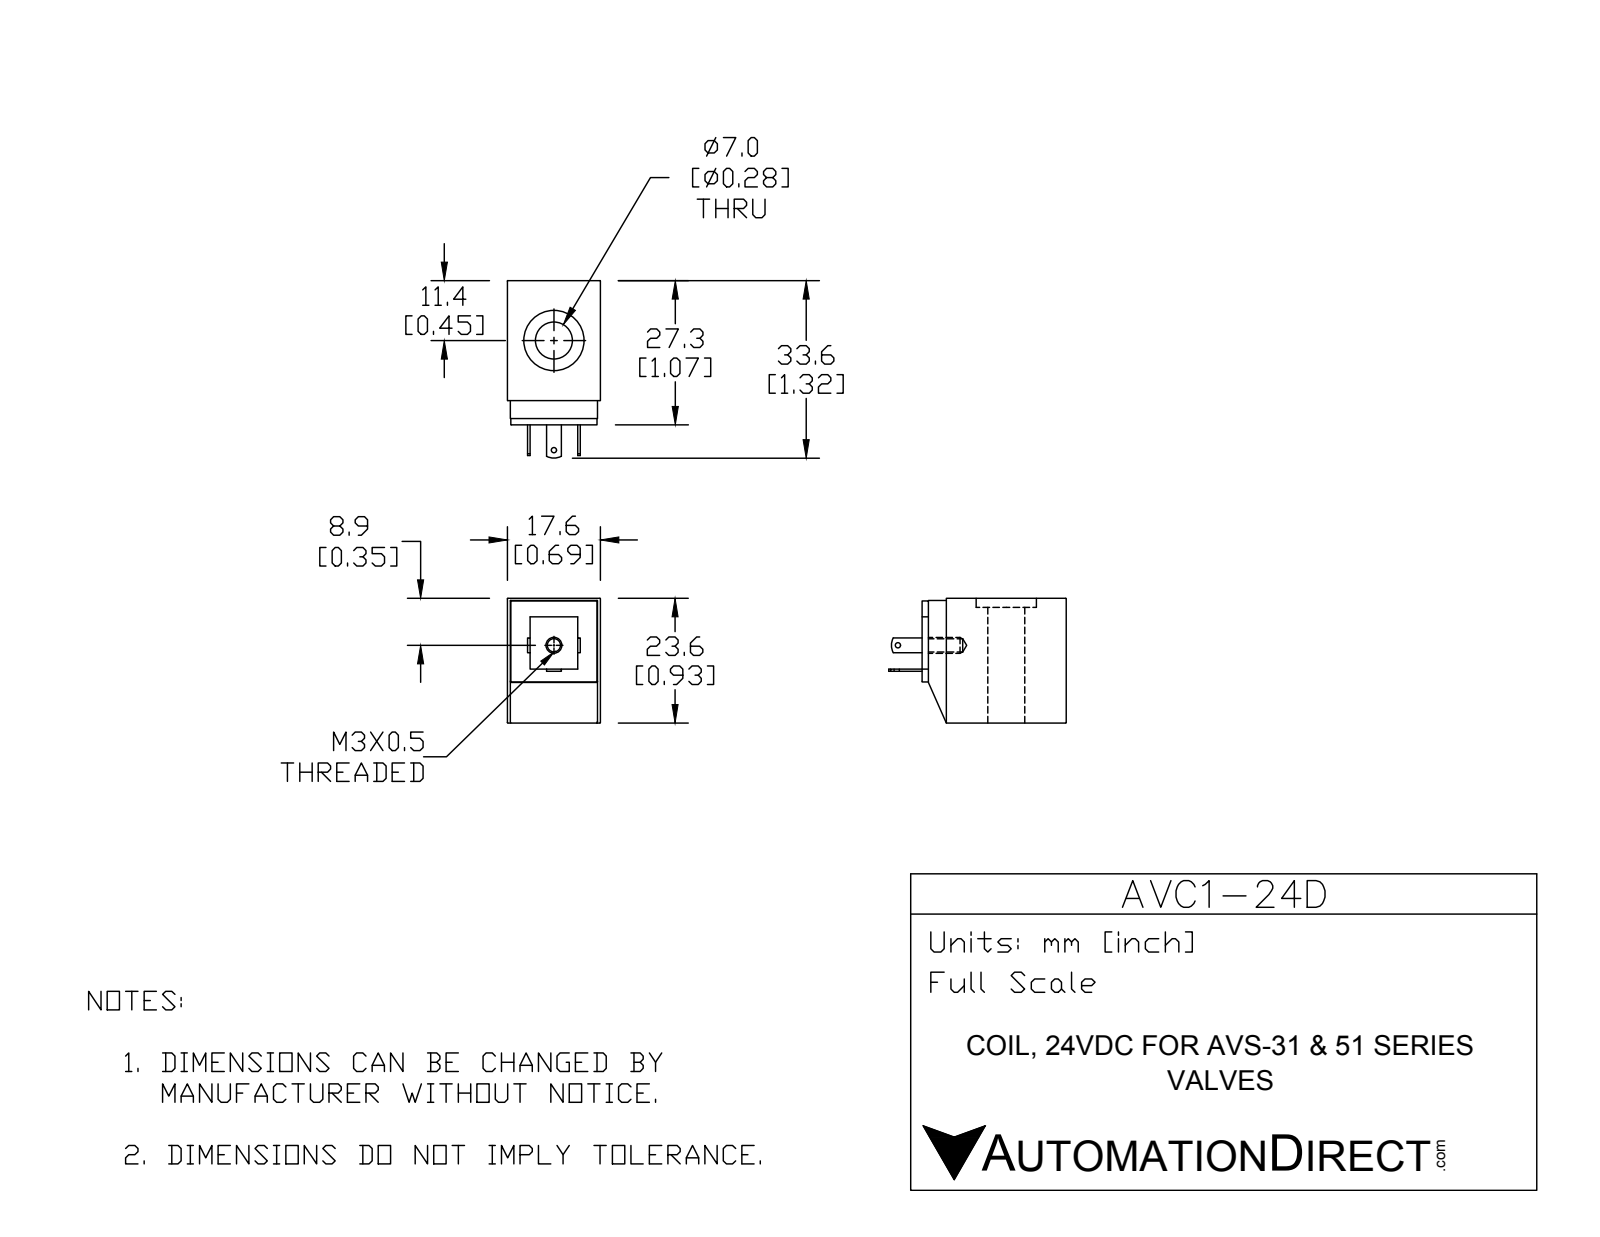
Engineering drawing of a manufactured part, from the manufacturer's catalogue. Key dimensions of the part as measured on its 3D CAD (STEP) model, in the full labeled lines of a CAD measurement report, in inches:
Part name (STEP PRODUCT): AVC1-24D
STEP written by: SolidWorks 2016 (AUTOMOTIVE_DESIGN)
Units: inches
Bodies: 1 solid, 69 faces (31 planar, 32 cylindrical, 6 other)
Overall size (bounding box): 1.323 × 0.929 × 0.693
Volume: 0.591 in³ · Surface area: 5.65 in²
Round holes (diameter × count): ⌀0.039 ×2, ⌀0.098 ×1, ⌀0.276 ×1, ⌀0.449 ×1
Partial cylindrical surfaces — rounded edges, fillets, slot ends (radius × count): R0.004 ×16, R0.118 ×2
Main face-to-face distances: 0.693, 0.929, 1.075, 0.022, 0.671, 0.047, 1.028, 0.524, 0.016, 0.65
Hole centre spacings: 0.817
